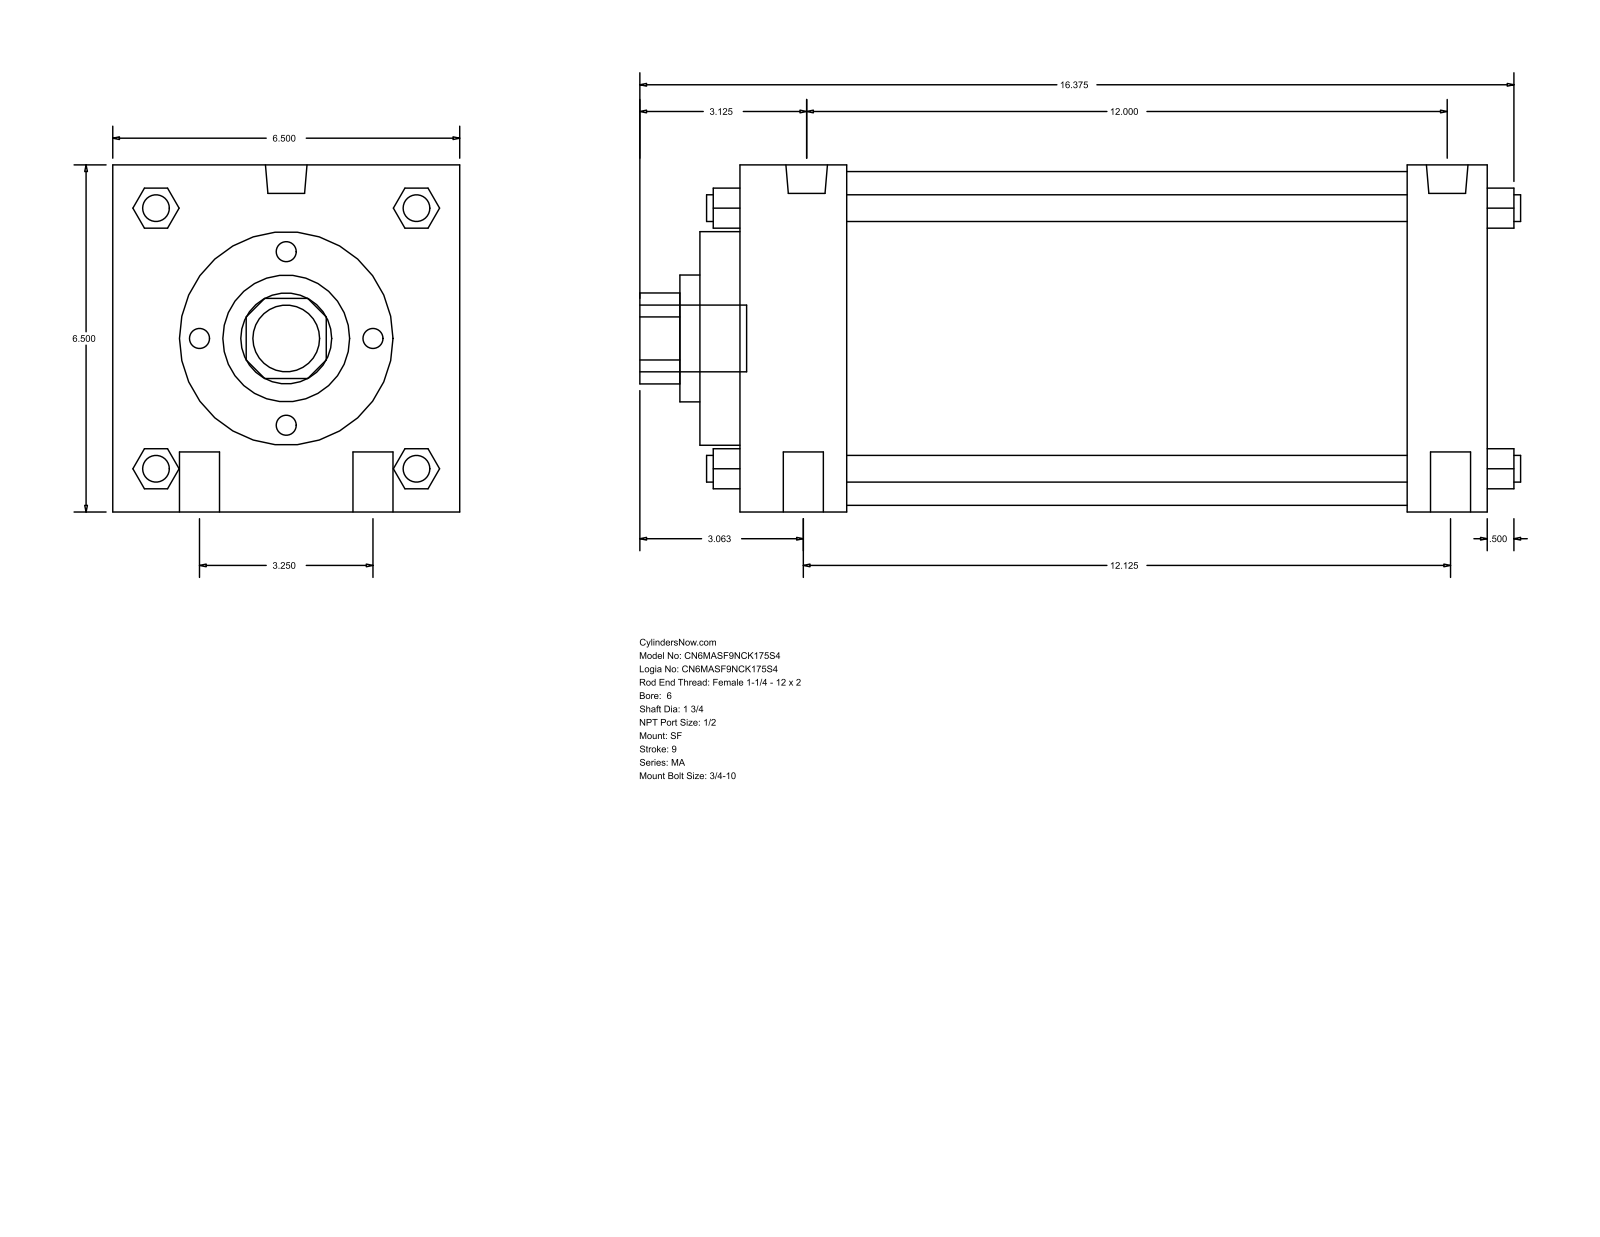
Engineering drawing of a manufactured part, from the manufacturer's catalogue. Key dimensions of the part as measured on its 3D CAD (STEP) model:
Part name (STEP PRODUCT): MA_SF__0600_1.75
STEP written by: GSSL Pune (CONFIG_CONTROL_DESIGN)
Units: millimetres
Bodies: 0 solids, 126 faces (95 planar, 31 cylindrical, 0 other)
Overall size (bounding box): 419.1 × 165.1 × 165.1
Round holes (diameter × count): ⌀44.45 ×1, ⌀60.33 ×1, ⌀101.6 ×1, ⌀158.75 ×1
Round bosses / shafts (diameter × count): ⌀19.05 ×4, ⌀12.7 ×4, ⌀19.77 ×2, ⌀17.46 ×2, ⌀31.75 ×1
Partial cylindrical surfaces — rounded edges, fillets, slot ends (radius × count): R21.63 ×1
Main face-to-face distances: 165.1, 355.61, 19.05, 50.8, 317.5, 38.11, 266.7, 304.81, 69.85, 336.55
